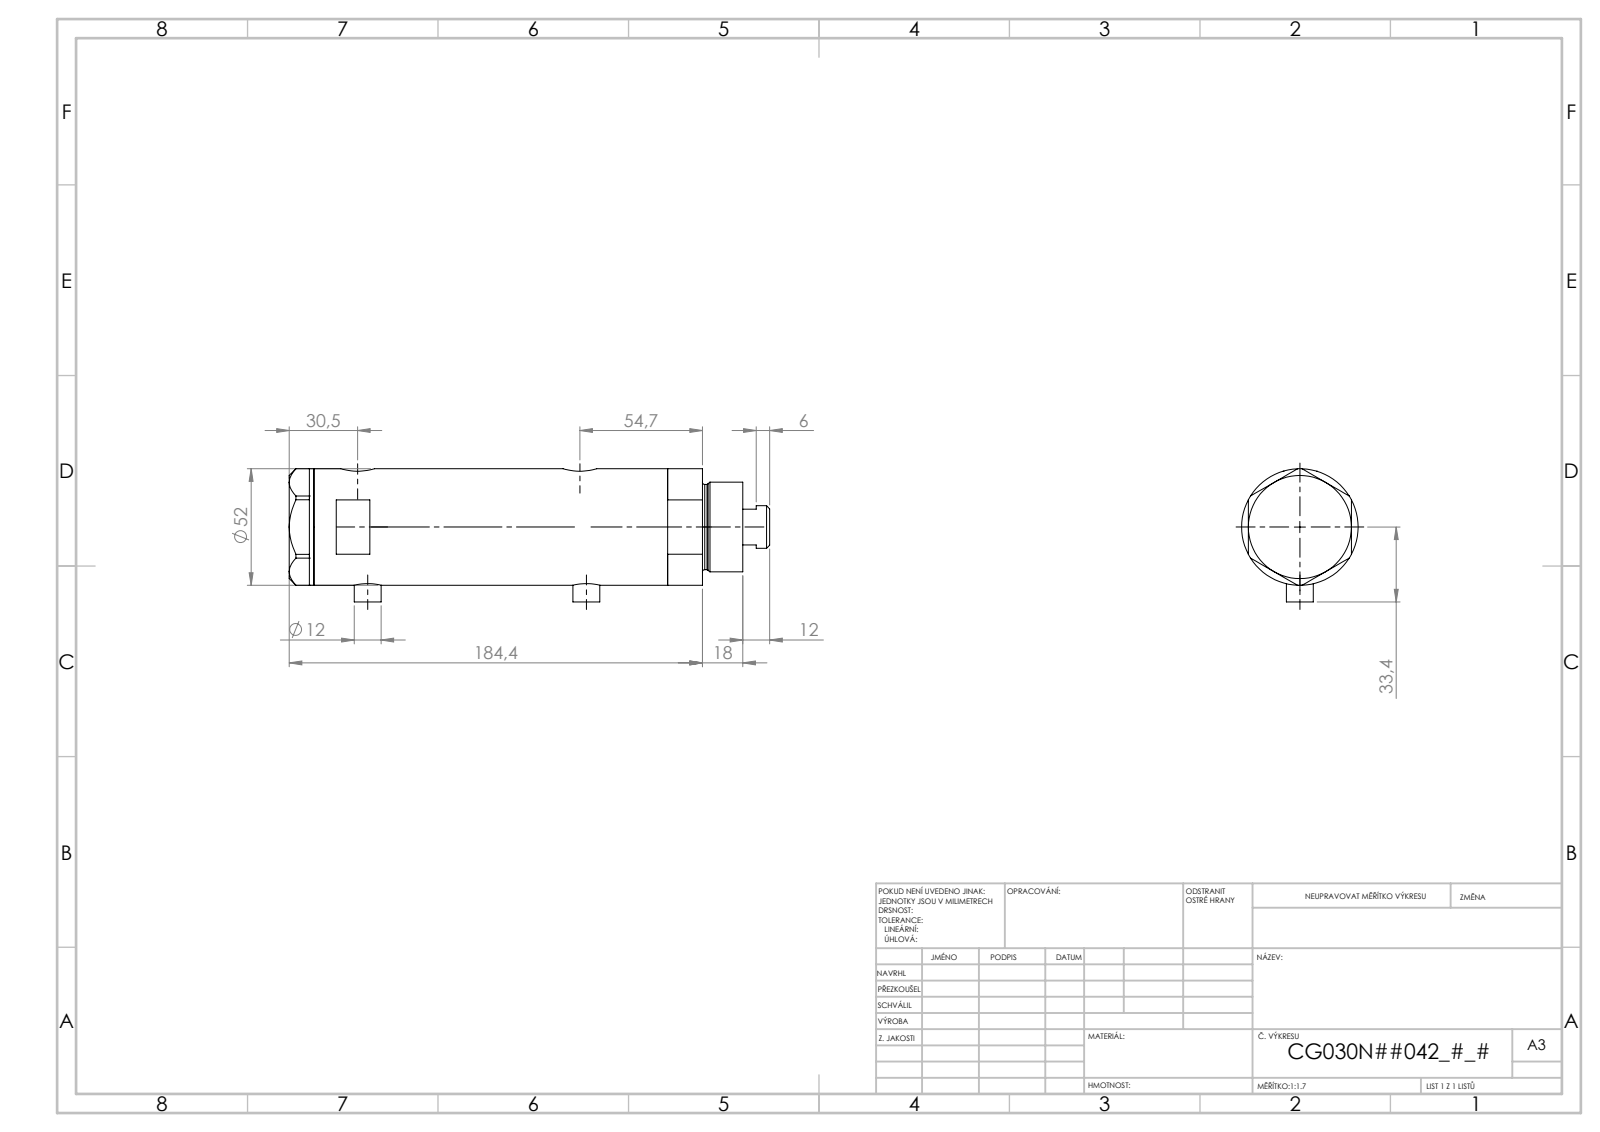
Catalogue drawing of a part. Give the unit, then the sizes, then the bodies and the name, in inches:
Units: inches
Overall size (bounding box): 7.52 × 2.091 × 2.047
Round holes (diameter × count): ⌀0.197 ×2, ⌀0.383 ×2, ⌀0.492 ×2, ⌀0.591 ×2, ⌀0.256 ×1, ⌀0.787 ×1, ⌀0.846 ×1, ⌀1.181 ×1, ⌀1.299 ×1, ⌀1.732 ×1
Round bosses / shafts (diameter × count): ⌀0.472 ×2, ⌀2.047 ×1, ⌀1.575 ×1, ⌀1.496 ×1, ⌀0.748 ×1
Main face-to-face distances: 3.761, 0.937, 2.824, 0.433, 1.37, 4.194, 1.811, 5.628, 5.194, 4.257
Hole centre spacings: 0.114, 0.177, 2.707, 2.821, 2.884, 2.998, 0.114, 0.115
Volume: 20.76 in³ · Surface area: 121.7 in²
Bodies: 4 solids, 140 faces (67 planar, 53 cylindrical, 20 other)
Part name (STEP PRODUCT): V270CG_MIDDLE; V270CG_VC; V270CG_BACK; V270CG_FRONT
STEP written by: SolidWorks 2019 (CONFIG_CONTROL_DESIGN)
